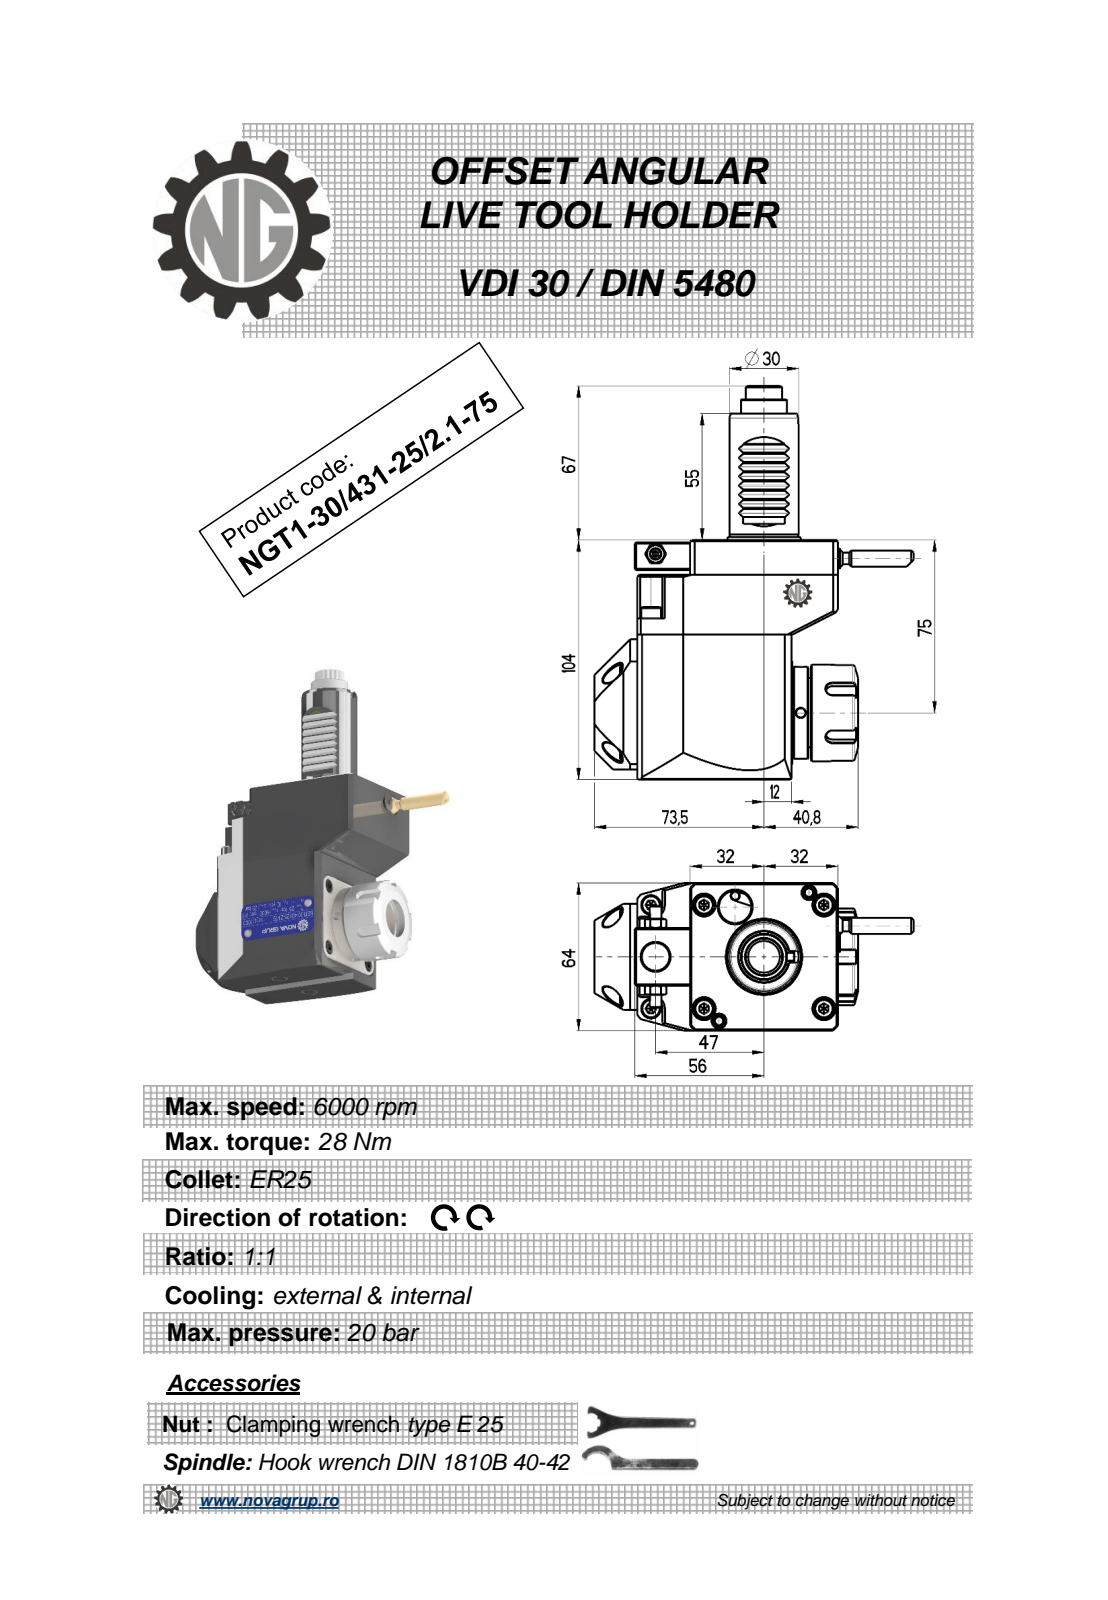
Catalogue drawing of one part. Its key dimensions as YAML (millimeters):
part_name: "NGT1_30_431_25_2_1_75"
step_written_by: "PRO/ENGINEER BY PARAMETRIC TECHNOLOGY CORPORATION, 2010280 (CONFIG_CONTROL_DESIGN)"
units: millimeters
bodies: {solids: 1, faces: 526, planar: 212, cylindrical: 157, other: 157}
overall_size: [171, 138.38, 65.4]
volume: 570752
surface_area: 55251
round_holes:
  - {diameter: 4, count: 2}
  - {diameter: 2.5, count: 1}
  - {diameter: 3, count: 1}
  - {diameter: 4.2, count: 1}
  - {diameter: 9.5, count: 1}
  - {diameter: 12, count: 1}
  - {diameter: 20.3, count: 1}
round_bosses_or_shafts:
  - {diameter: 8.96, count: 2}
  - {diameter: 5, count: 2}
  - {diameter: 42, count: 1}
  - {diameter: 40, count: 1}
  - {diameter: 33, count: 1}
  - {diameter: 30, count: 1}
  - {diameter: 20, count: 1}
  - {diameter: 7, count: 1}
partial_cylinders:
  - {radius: 1.98, count: 36}
  - {radius: 0.26, count: 12}
  - {radius: 0.3, count: 8}
  - {radius: 3, count: 5}
  - {radius: 4, count: 2}
  - {radius: 7.08, count: 1}
  - {radius: 7.92, count: 1}
  - {radius: 13, count: 1}
face_to_face_distances: [64, 104, 87, 19.8, 20, 67.2, 15, 89, 67, 1]
hole_center_spacings: [13.54, 62.95, 68, 68.35, 93.4]
